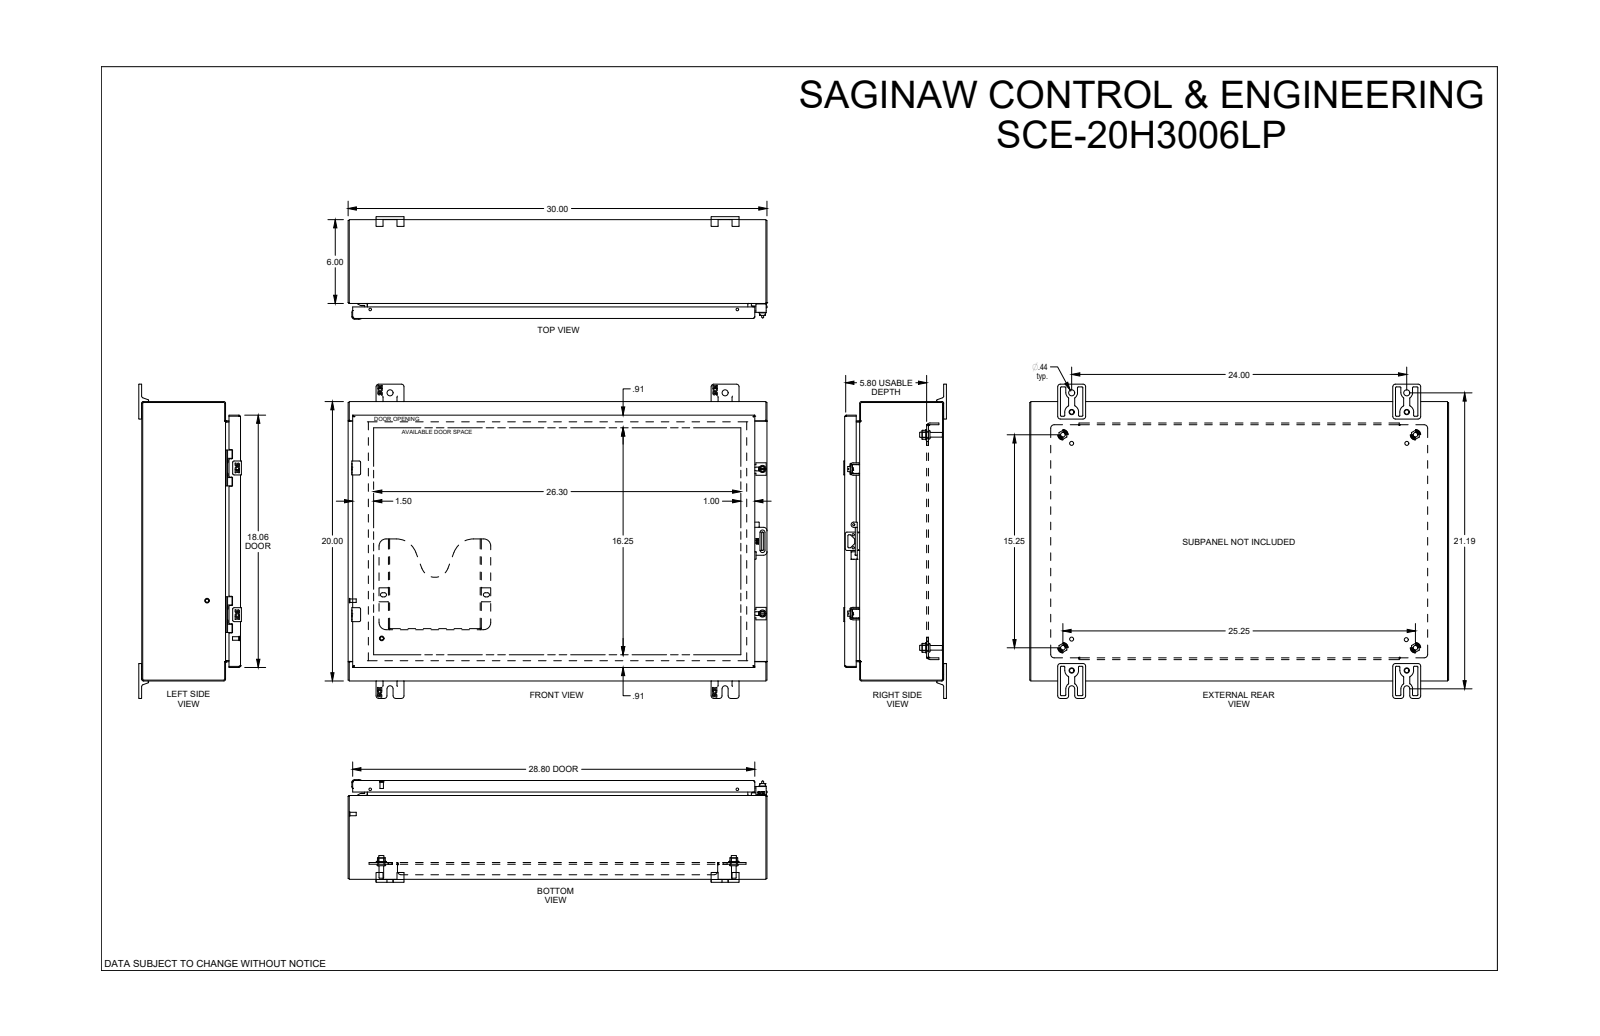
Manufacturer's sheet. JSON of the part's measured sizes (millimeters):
{"part_name": "SCE-20H3006LP", "step_written_by": "SolidWorks 2019 (CONFIG_CONTROL_DESIGN)", "units": "millimeters", "bodies": {"solids": 0, "faces": 4479, "planar": 1685, "cylindrical": 1187, "other": 1607}, "overall_size": [762, 571.5, 186.6], "round_holes": [[6.4, 5], [4.4, 4], [5.2, 4], [5.5, 4], [6.2, 4], [6.8, 4], [7.1, 4], [7.9, 4], [7.9, 4], [9.3, 4], [9.5, 4], [11.1, 4]], "round_bosses_or_shafts": [[6.3, 7], [4.3, 7], [6.4, 6], [14.3, 5], [15, 4], [9.6, 4], [9.3, 4], [8.4, 4]], "partial_cylinders_radius": [[0.6, 127], [0.3, 114], [1.6, 57], [0.4, 48], [0.8, 37], [0.7, 30], [1.5, 30], [4.7, 21]], "face_to_face_distances": [1.9, 177.7, 175.8, 1.9, 179.7, 177.7, 28.6, 150.4, 30.5, 147.3], "hole_center_spacings": [266.7, 0.5, 12.5, 25, 44.2, 57, 412.9, 428.9]}
